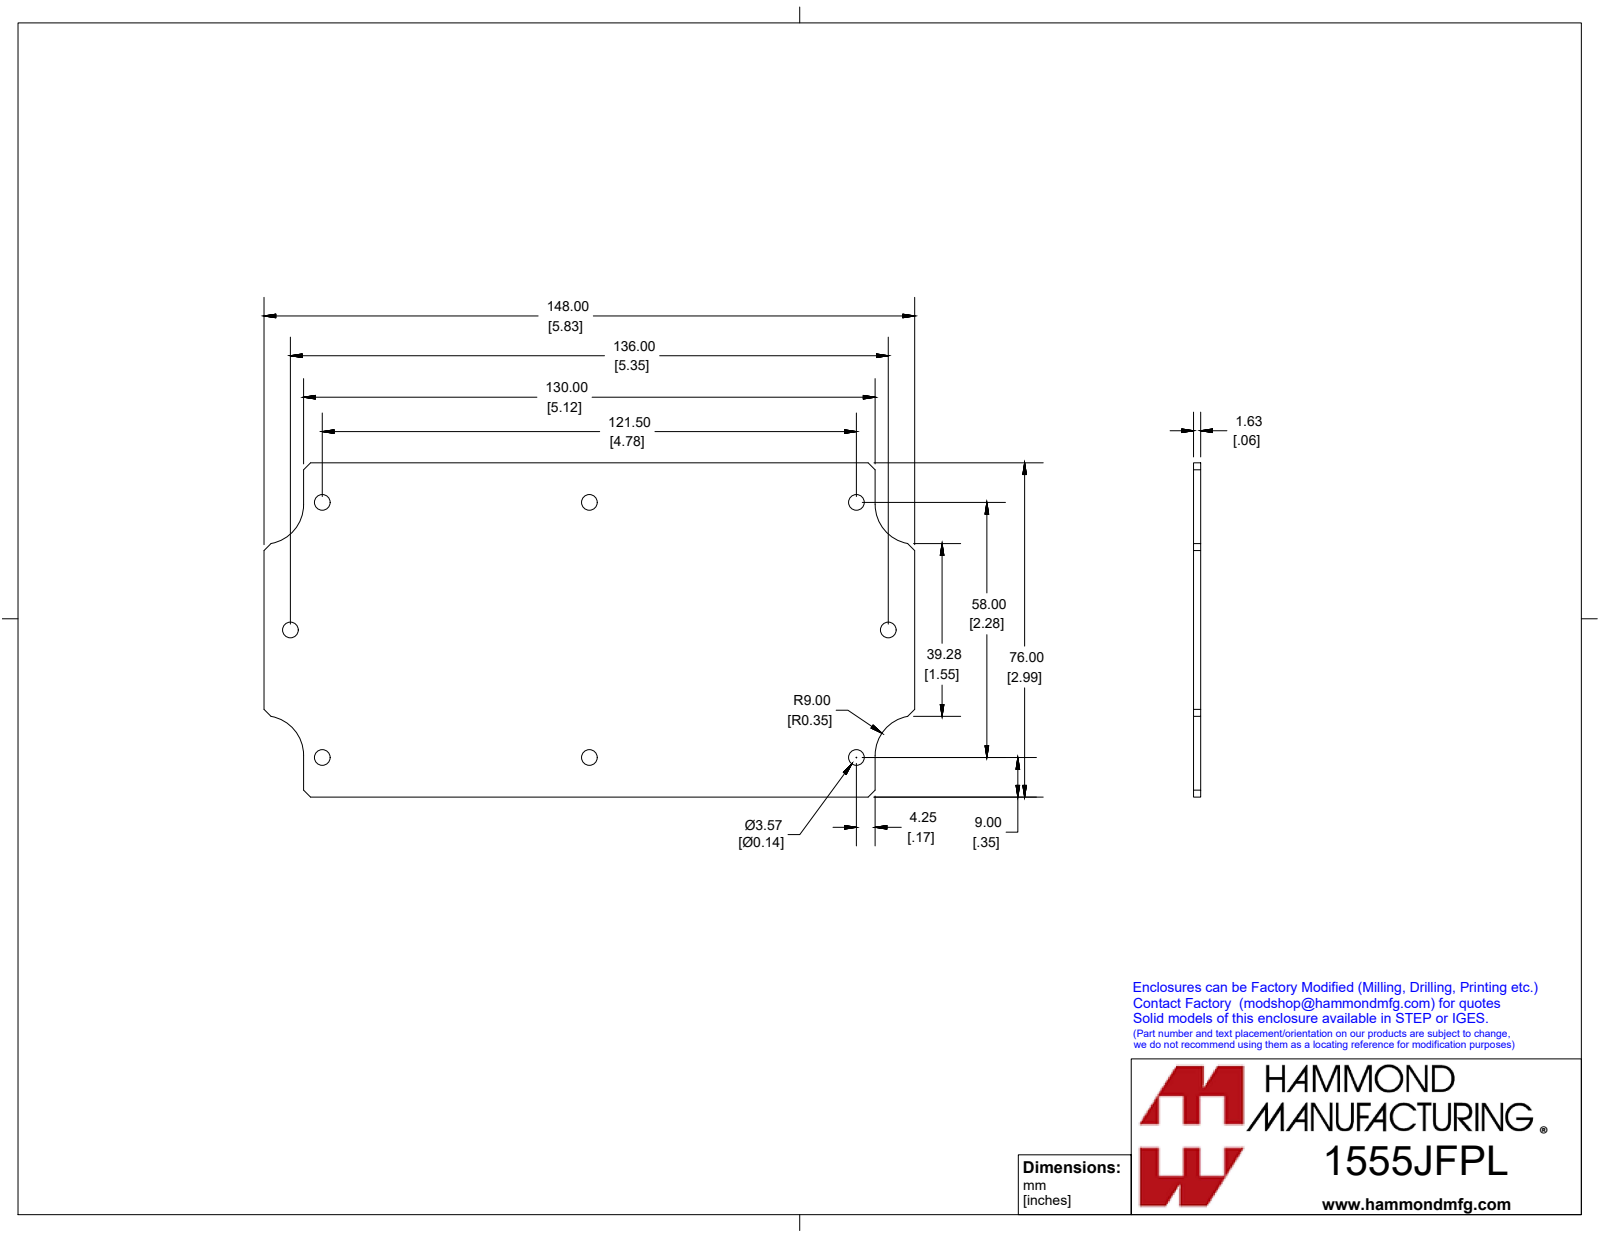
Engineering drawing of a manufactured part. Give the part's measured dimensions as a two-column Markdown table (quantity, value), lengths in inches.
| quantity | value |
| --- | --- |
| part name | 1555JFPL |
| STEP written by | SolidWorks 2019 (CONFIG_CONTROL_DESIGN) |
| units | inches |
| bodies | 1 solid, 30 faces (18 planar, 12 cylindrical, 0 other) |
| overall size | 5.827 × 2.992 × 0.064 |
| volume | 1.05 in³ |
| surface area | 34.08 in² |
| round holes (diameter × count) | 0.118 × 8 |
| partial cylindrical surfaces (radius × count) | 0.354 × 4 |
| main face-to-face distances | 0.064, 2.992, 5.827, 0.354, 5.472, 5.118, 5.385, 0.261, 5.646, 5.124 |
| hole center spacings | 1.177, 2.392, 2.911, 3.307, 5.196, 2.283, 4.783, 5.3 |
